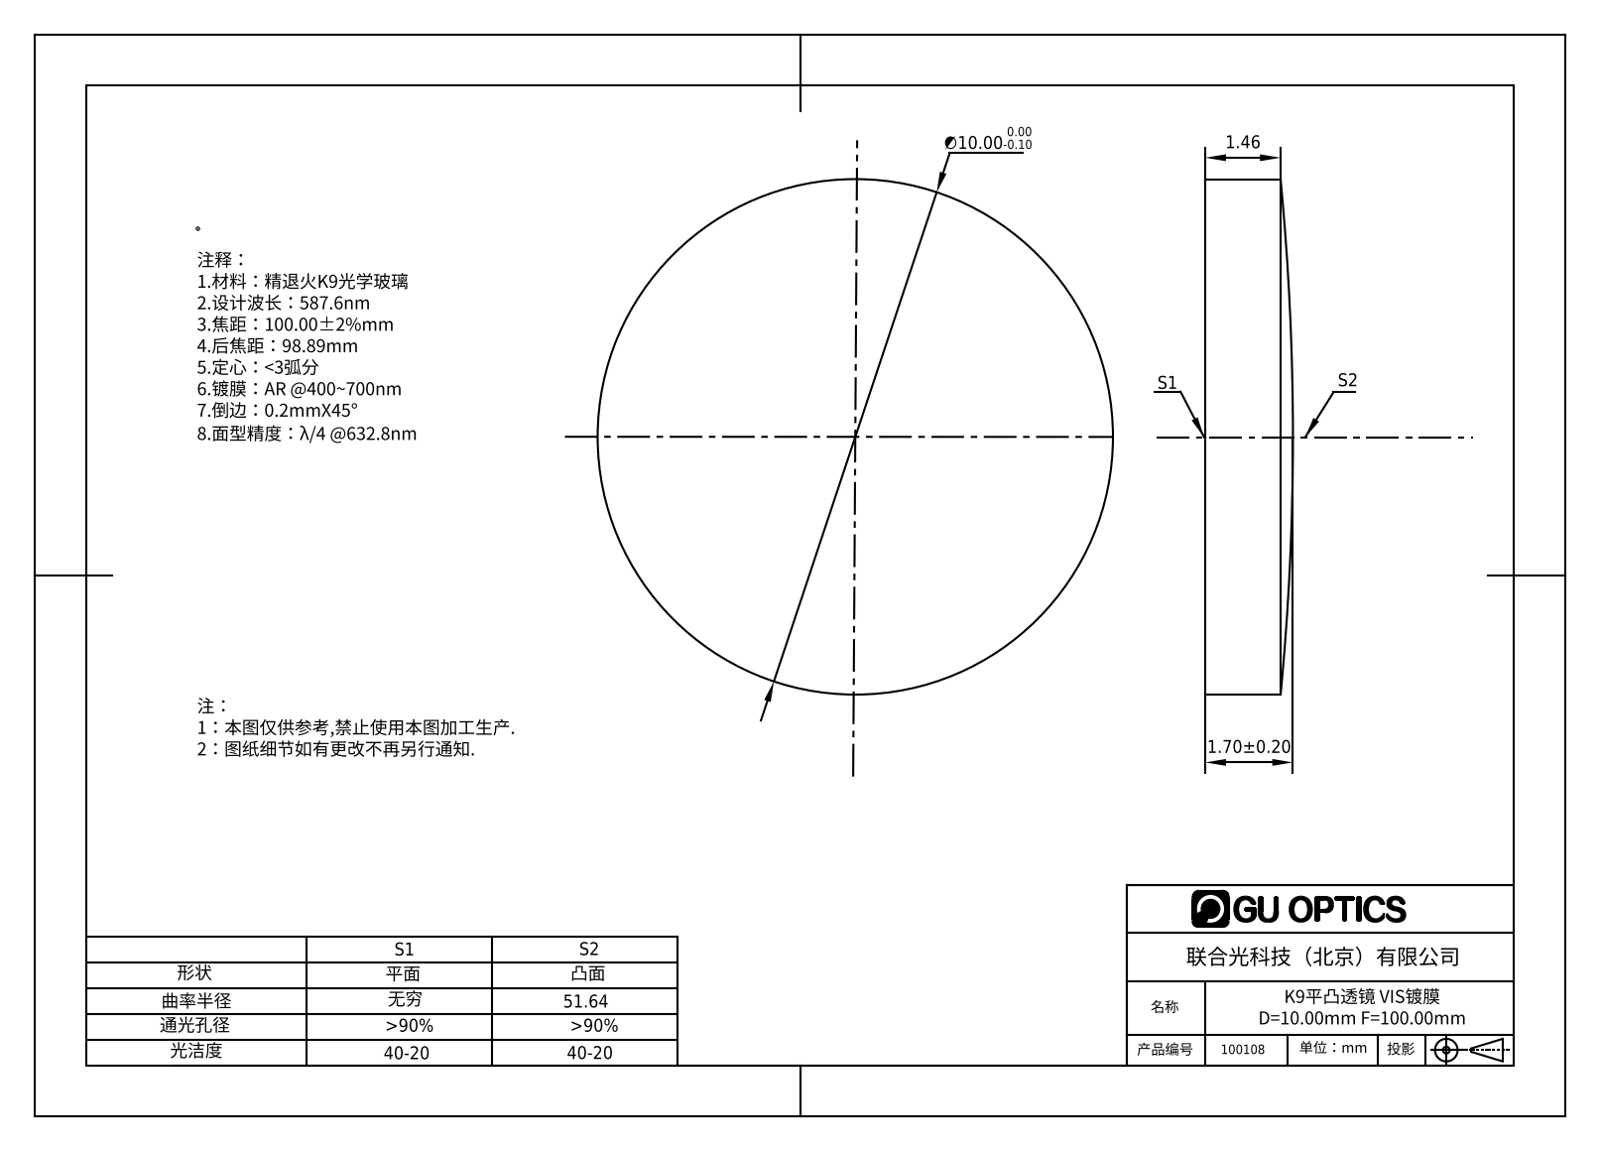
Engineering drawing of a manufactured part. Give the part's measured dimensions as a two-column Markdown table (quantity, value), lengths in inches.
| quantity | value |
| --- | --- |
| part name | 100108 |
| STEP written by | SolidWorks 2016 (AUTOMOTIVE_DESIGN) |
| units | inches |
| bodies | 1 solid, 5 faces (1 planar, 2 cylindrical, 2 other) |
| overall size | 0.394 × 0.394 × 0.067 |
| volume | 0.008 in³ |
| surface area | 0.315 in² |
| round bosses / shafts (diameter × count) | 0.394 × 1 |
